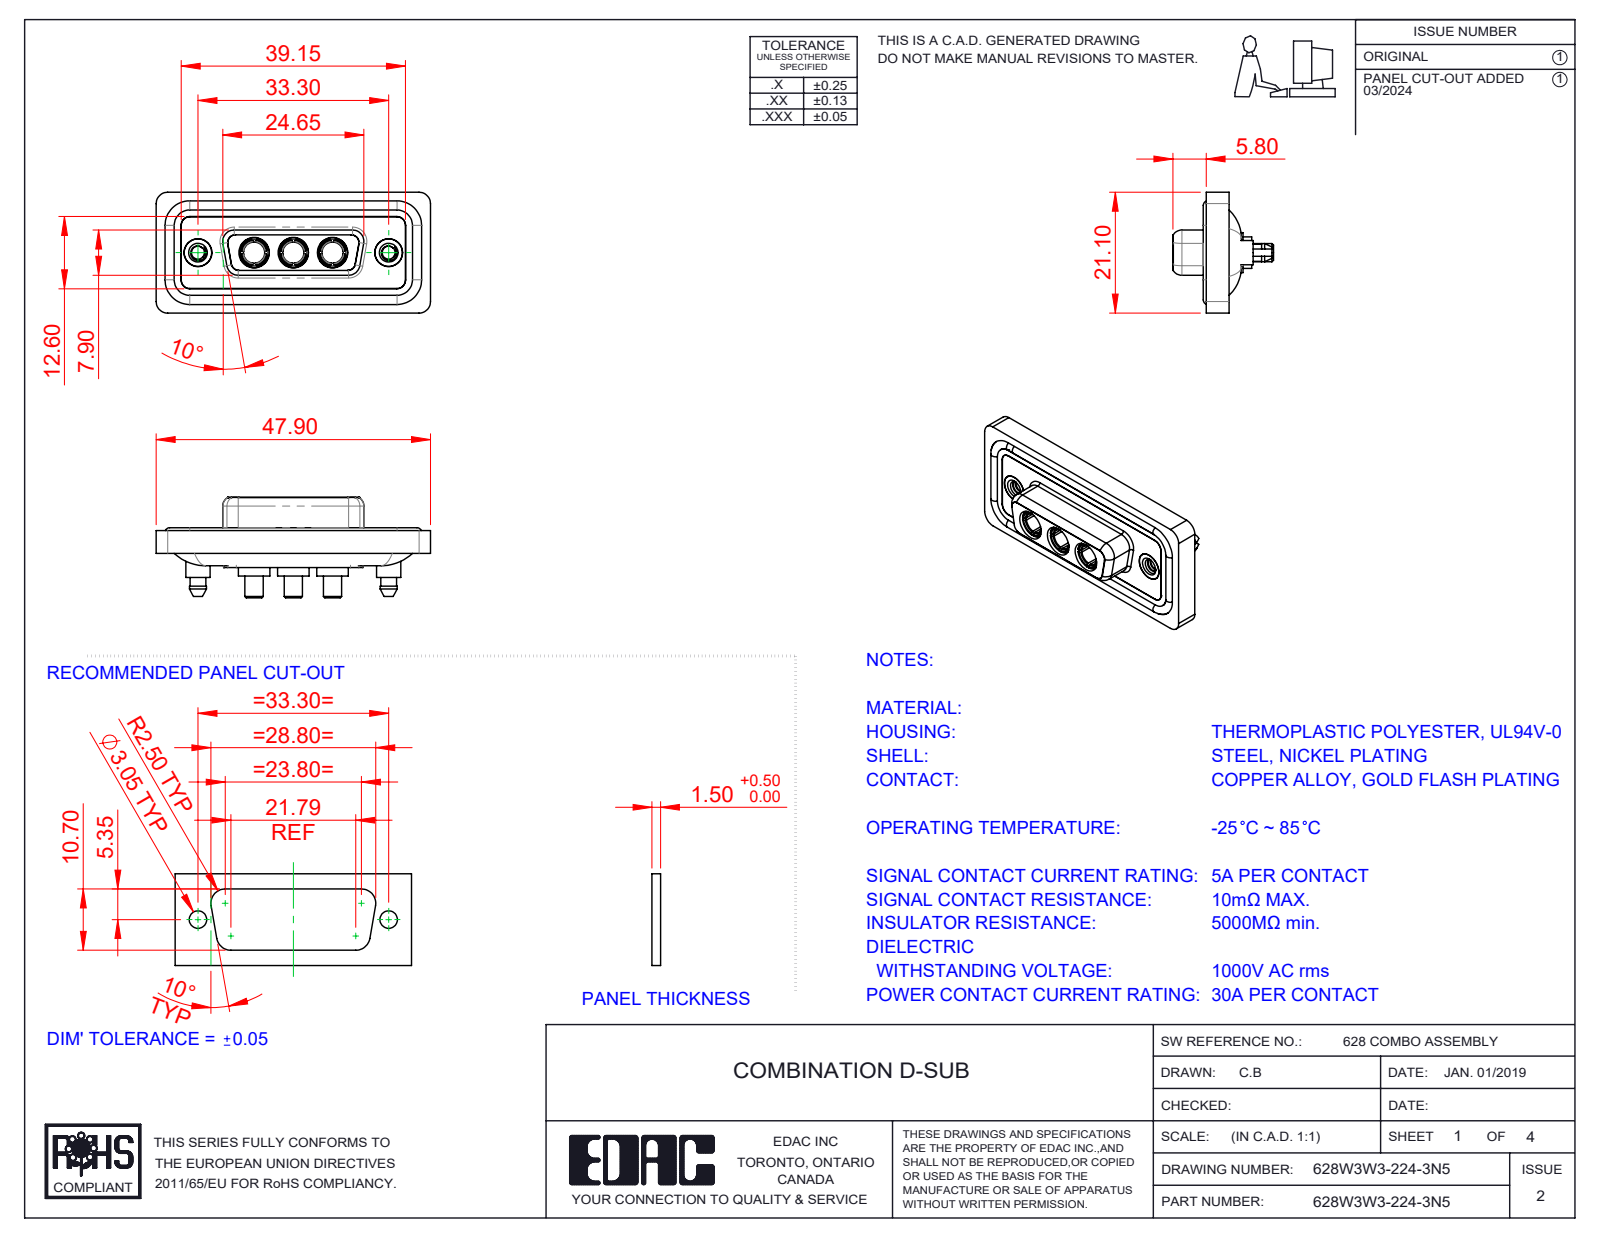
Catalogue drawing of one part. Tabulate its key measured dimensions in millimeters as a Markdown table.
| quantity | value |
| --- | --- |
| part name | 628W3W3-224-3N5; Power Socket_30A S; 628Combo Threaded Boardlock_5; 628Combo Housing_3W3 (+3 more) |
| STEP written by | SolidWorks 2023 (CONFIG_CONTROL_DESIGN) |
| units | millimeters |
| bodies | 13 solids, 658 faces (208 planar, 289 cylindrical, 161 other) |
| overall size | 47.9 × 21.1 × 17.55 |
| volume | 6 181 mm³ |
| surface area | 10 085 mm² |
| round holes (diameter × count) | 4.85 × 5, 3.7 × 3, 5.3 × 3, 2.26 × 2, 4 × 2, 4.05 × 2, 5 × 2 |
| round bosses / shafts (diameter × count) | 1.6 × 4, 5.5 × 3, 5.2 × 3, 4.96 × 3, 4.75 × 3, 3.75 × 3, 3.2 × 3, 5.4 × 2 |
| partial cylindrical surfaces (radius × count) | 1.5 × 24, 2 × 20, 1.35 × 12, 1.6 × 10, 0.25 × 4, 0.5 × 4, 0.6 × 4, 0.65 × 4 |
| main face-to-face distances | 0.4, 1.8, 1.6, 0.5, 7.45, 1.1, 2.9, 5.65, 7.05, 6.6 |
| hole center spacings | 6.85, 9.8, 16.65, 23.5, 13.7, 33.3 |
